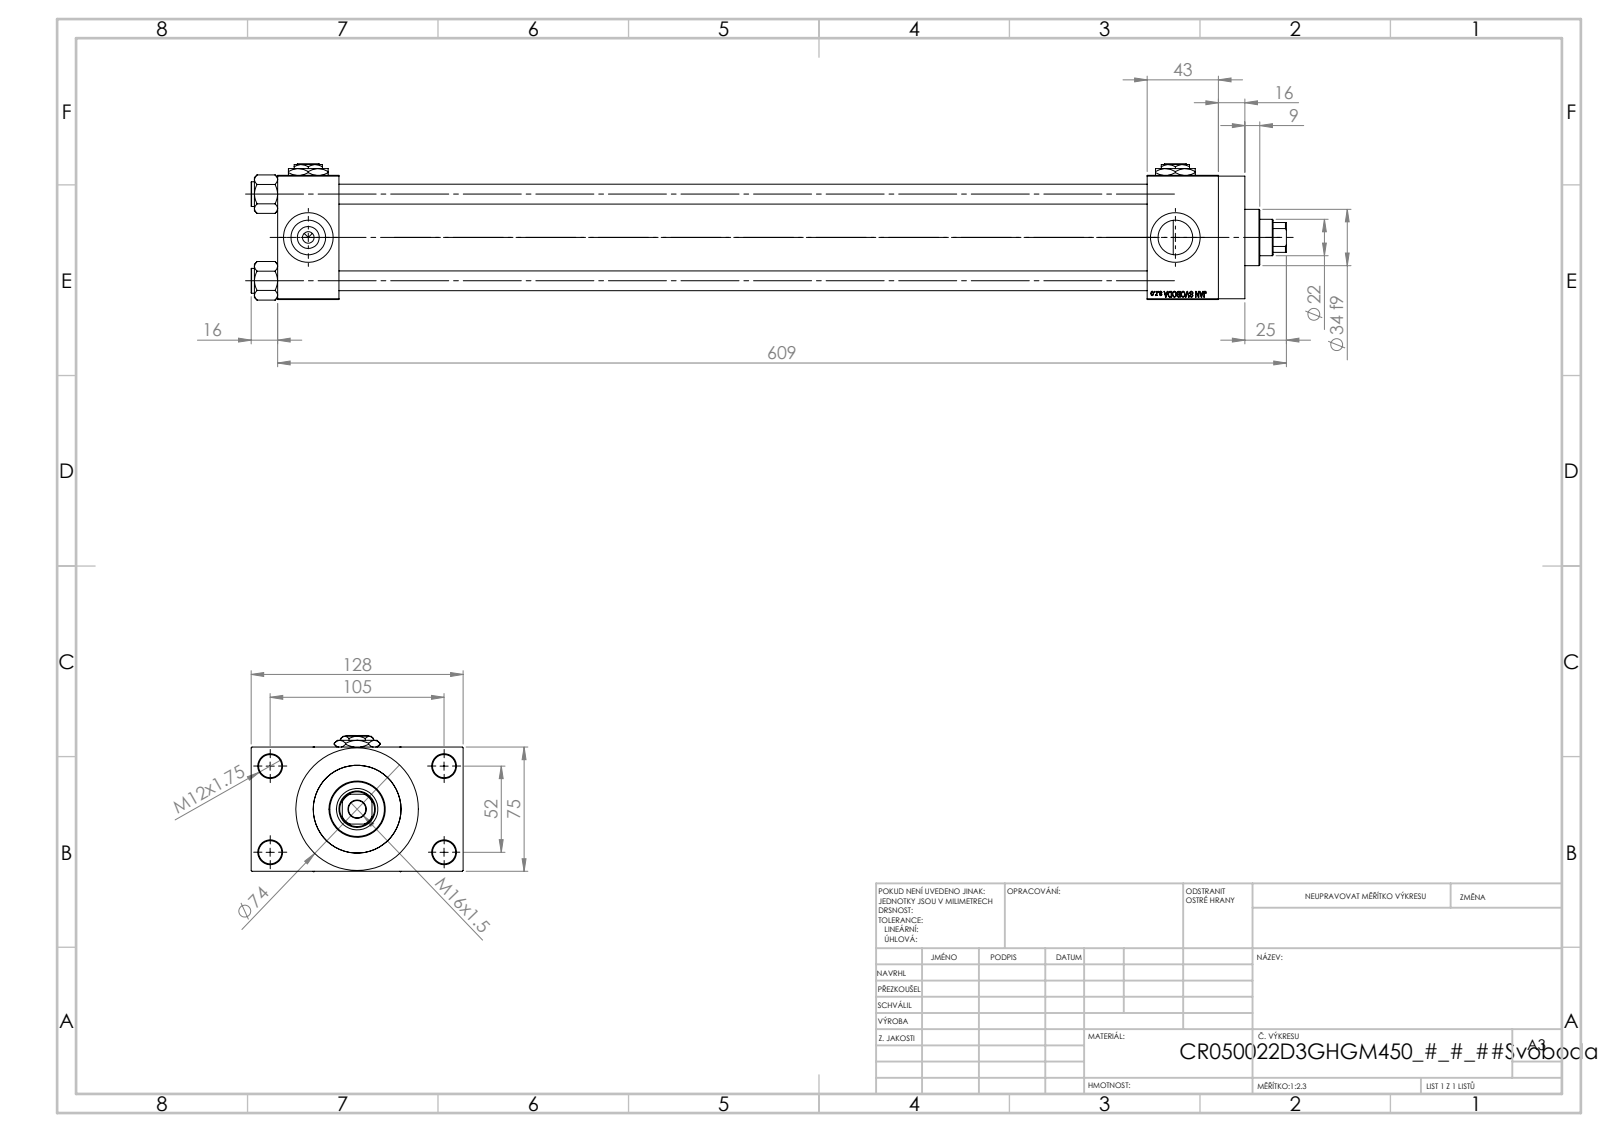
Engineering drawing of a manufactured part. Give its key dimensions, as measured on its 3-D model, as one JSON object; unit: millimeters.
{"part_name": "NUT_M5_D; Zatka_pro_OIL_PORT; V215CR_D_TYCINKA; V215CR_D_Body (+2 more)", "step_written_by": "SolidWorks 2019 (CONFIG_CONTROL_DESIGN)", "units": "millimeters", "bodies": {"solids": 13, "faces": 1204, "planar": 545, "cylindrical": 99, "other": 560}, "overall_size": [625, 128, 82.27], "volume_mm3": 1366000, "surface_area_mm2": 408677, "round_holes": [[12, 4], [14, 4], [20.96, 4], [30, 4], [7, 3], [10.5, 1], [22, 1], [25, 1], [41, 1], [50, 1], [53, 1]], "round_bosses_or_shafts": [[15, 4], [74, 1], [56, 1], [34, 1]], "partial_cylinders_radius": [[10.5, 1]], "face_to_face_distances": [75, 488, 37, 525, 26.5, 568, 531, 43, 101.5, 16], "hole_center_spacings": [26.35, 36.98, 52.3, 58.43, 58.59, 78.65, 94.37, 52]}
